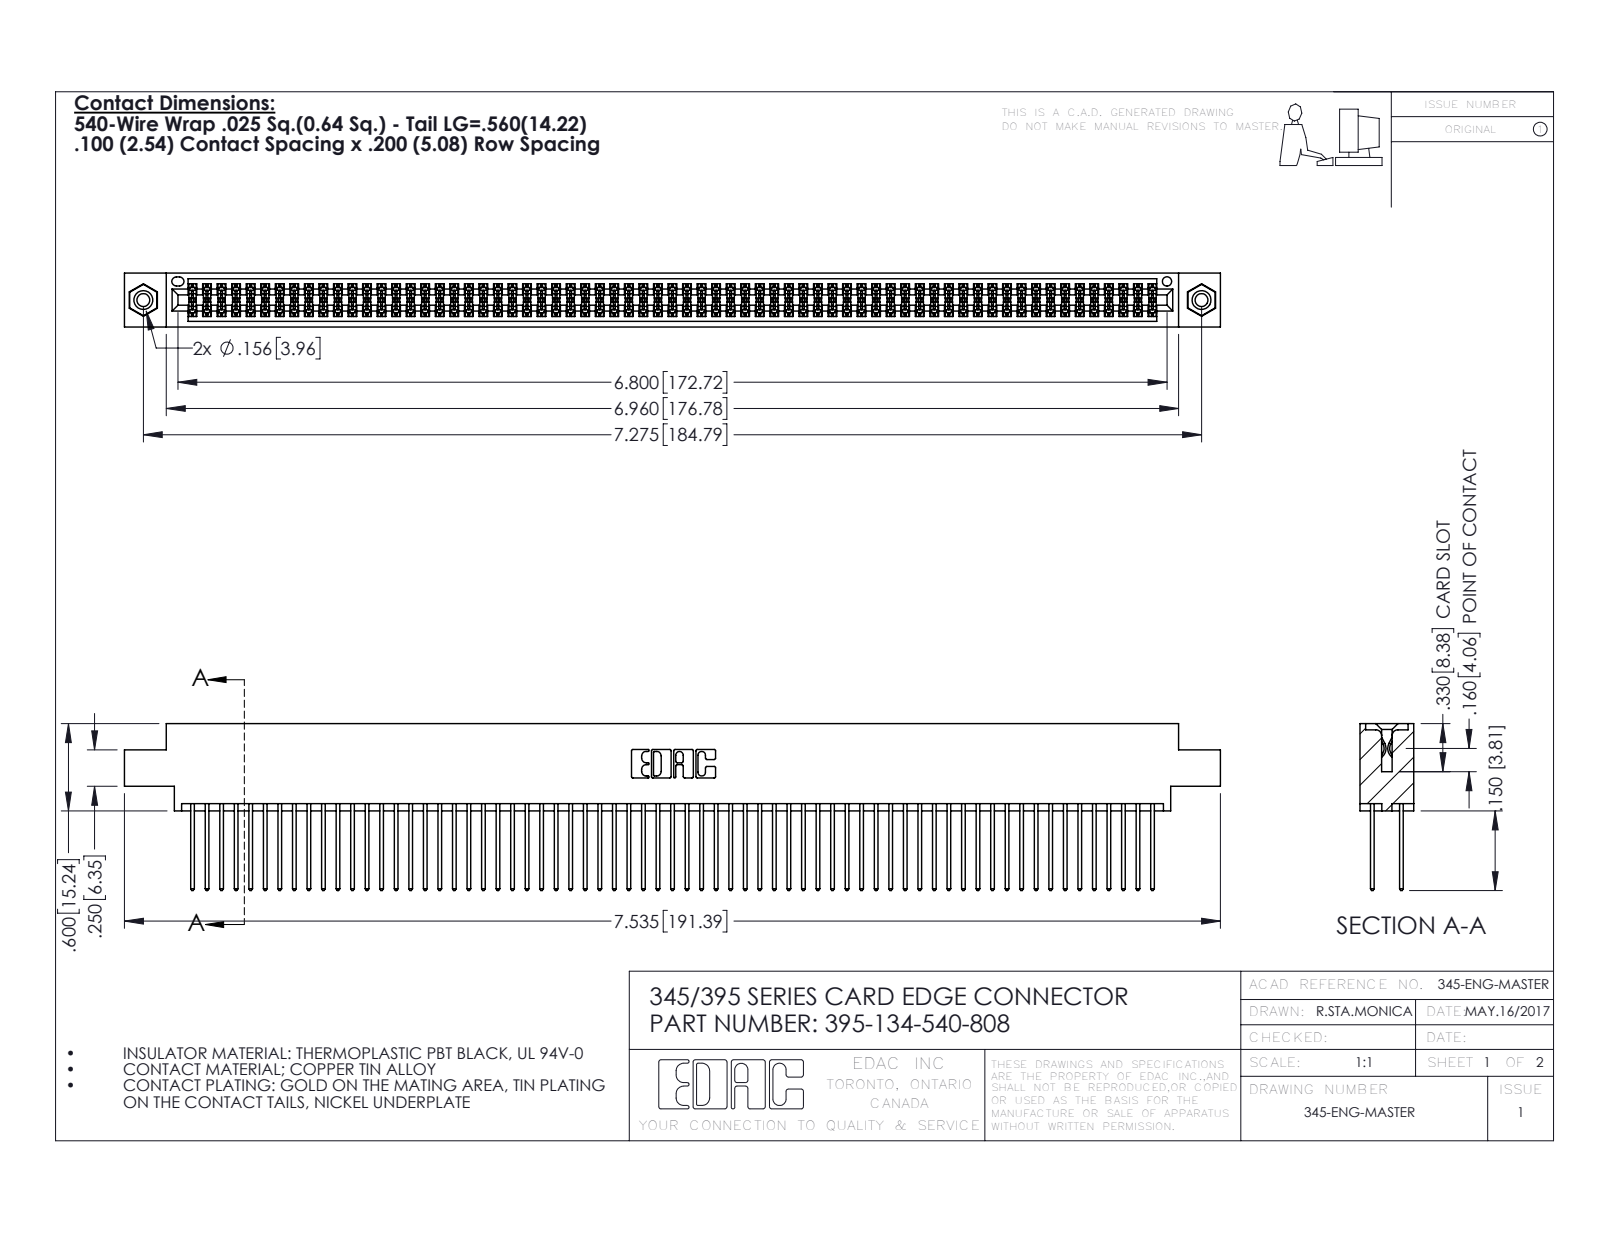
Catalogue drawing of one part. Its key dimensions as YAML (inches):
part_name: "345-250-001_345-250-003-102; 345 Part_0.170 Offset - 0.156 Dia-TI; 395-134-540-808; 345-292-001_345-293-140"
step_written_by: "SolidWorks 2016 (CONFIG_CONTROL_DESIGN)"
units: inches
bodies: {solids: 137, faces: 6890, planar: 4538, cylindrical: 2336, other: 16}
overall_size: [7.535, 1.147, 0.37]
volume: 1.172
surface_area: 48.66
round_holes:
  - {diameter: 0.089, count: 2}
  - {diameter: 0.125, count: 2}
  - {diameter: 0.156, count: 2}
  - {diameter: 0.064, count: 1}
round_bosses_or_shafts:
  - {diameter: 0.155, count: 2}
partial_cylinders:
  - {radius: 0.006, count: 201}
  - {radius: 0.01, count: 134}
  - {radius: 0.01, count: 22}
  - {radius: 0.007, count: 6}
  - {radius: 0.031, count: 6}
  - {radius: 0.026, count: 3}
  - {radius: 0.014, count: 2}
  - {radius: 0.019, count: 2}
face_to_face_distances: [0.072, 0.298, 0.2, 0.098, 0.272, 0.025, 0.37, 0.225, 0.175, 0.149]
hole_center_spacings: [0.27, 7.039, 7.275]
